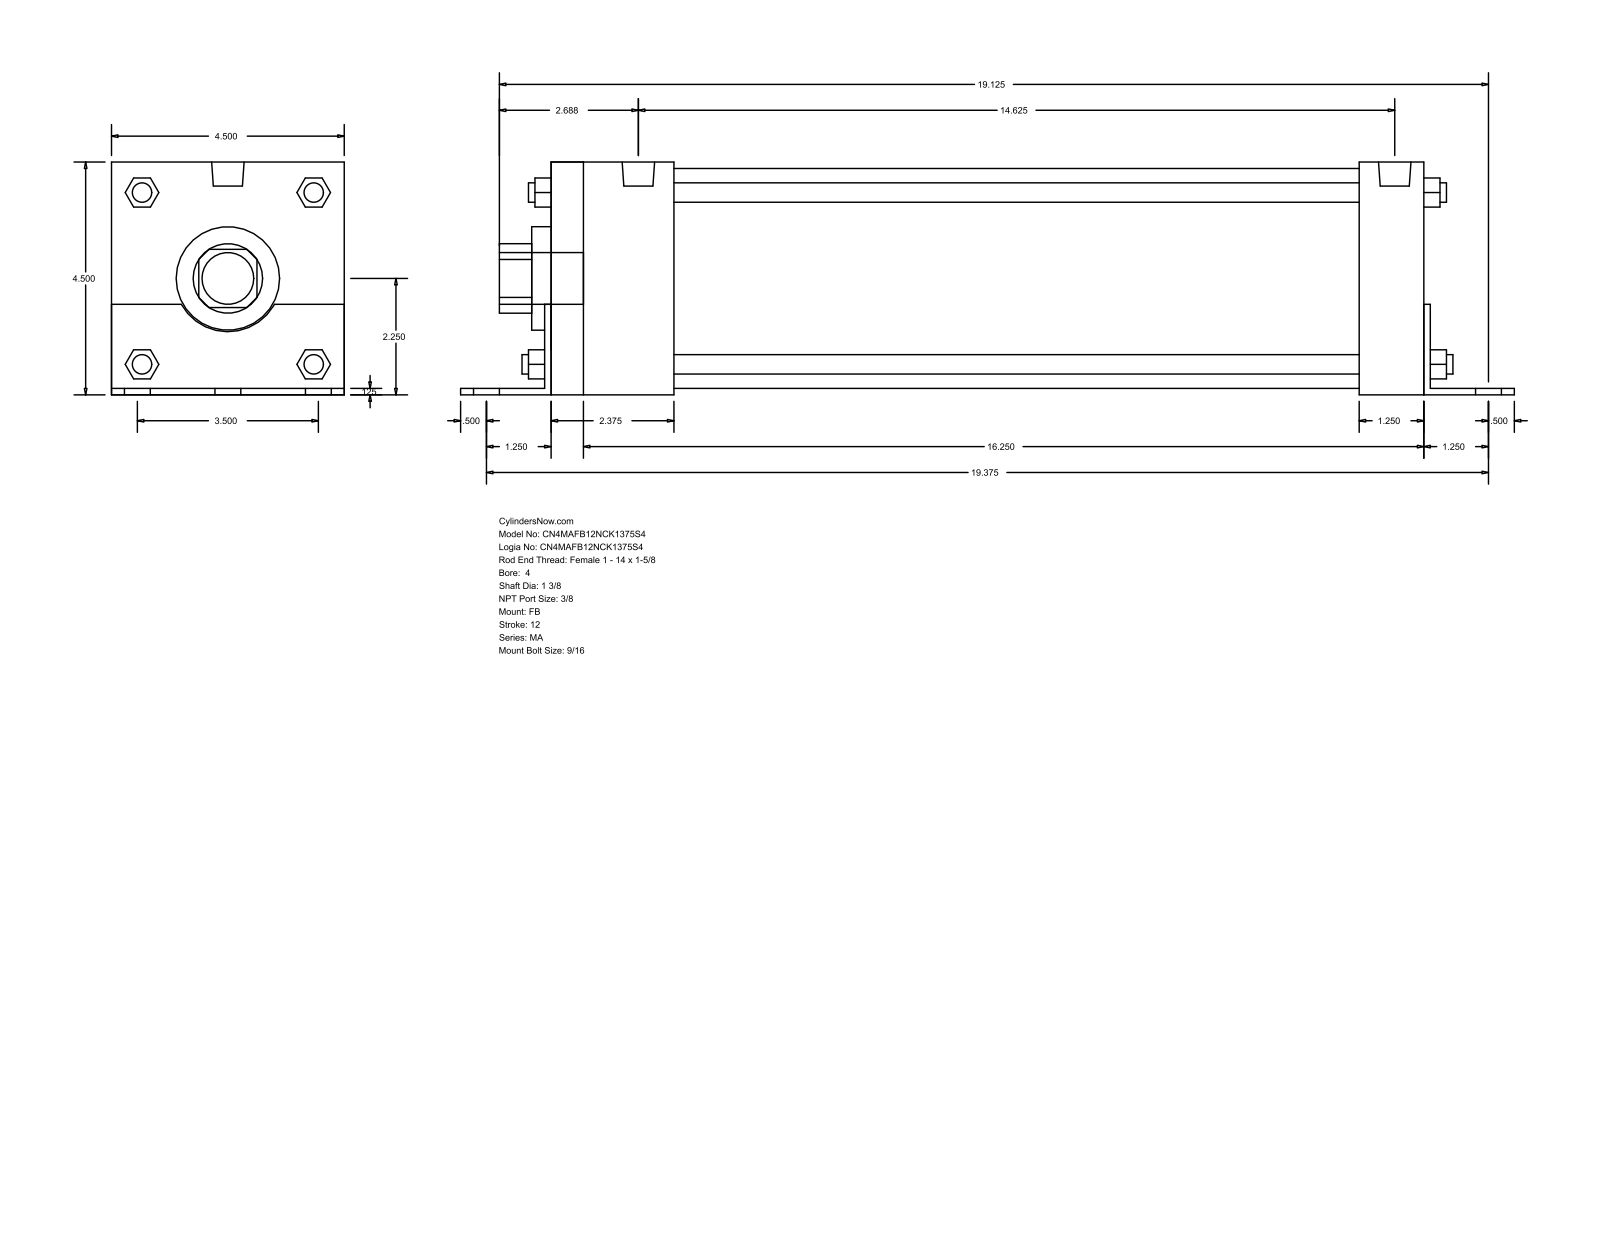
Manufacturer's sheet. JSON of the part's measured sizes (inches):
{"part_name": "MA_FB__0400_1.375", "step_written_by": "GSSL Pune (CONFIG_CONTROL_DESIGN)", "units": "inches", "bodies": {"solids": 0, "faces": 140, "planar": 105, "cylindrical": 35, "other": 0}, "overall_size": [20.375, 4.502, 4.5], "round_holes": [[1.375, 1], [2, 1], [4.25, 1]], "round_bosses_or_shafts": [[0.563, 6], [0.437, 4], [0.375, 4], [0.627, 2], [1, 1]], "partial_cylinders_radius": [[0.672, 1], [1.03, 1]], "face_to_face_distances": [4.5, 0.125, 4.502, 0.123, 4.377, 16.875, 0.125, 17, 1.375, 2.375]}
